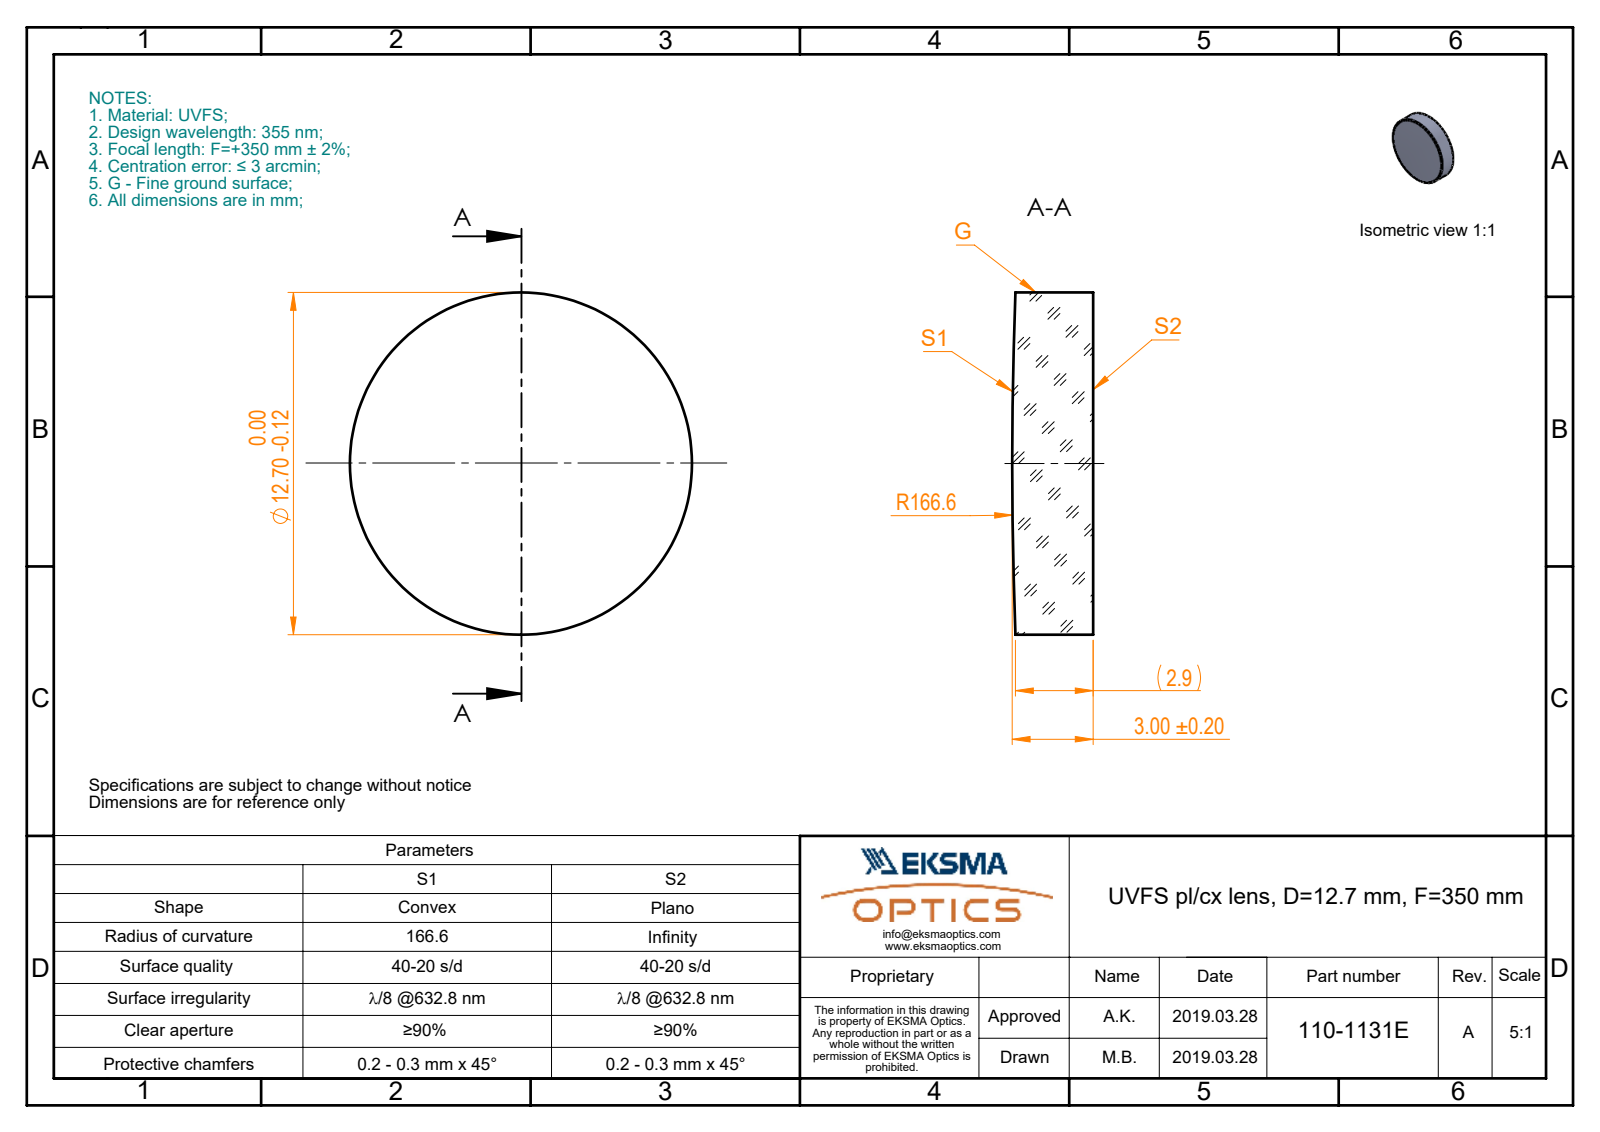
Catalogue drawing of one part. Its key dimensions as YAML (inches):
part_name: "110-1131E UVFS pl-cx 12.7 F350"
step_written_by: "SolidWorks 2017 (CONFIG_CONTROL_DESIGN)"
units: inches
bodies: {solids: 1, faces: 5, planar: 1, cylindrical: 2, other: 2}
overall_size: [0.5, 0.5, 0.118]
volume: 0.023
surface_area: 0.57
round_bosses_or_shafts:
  - {diameter: 0.5, count: 1}
